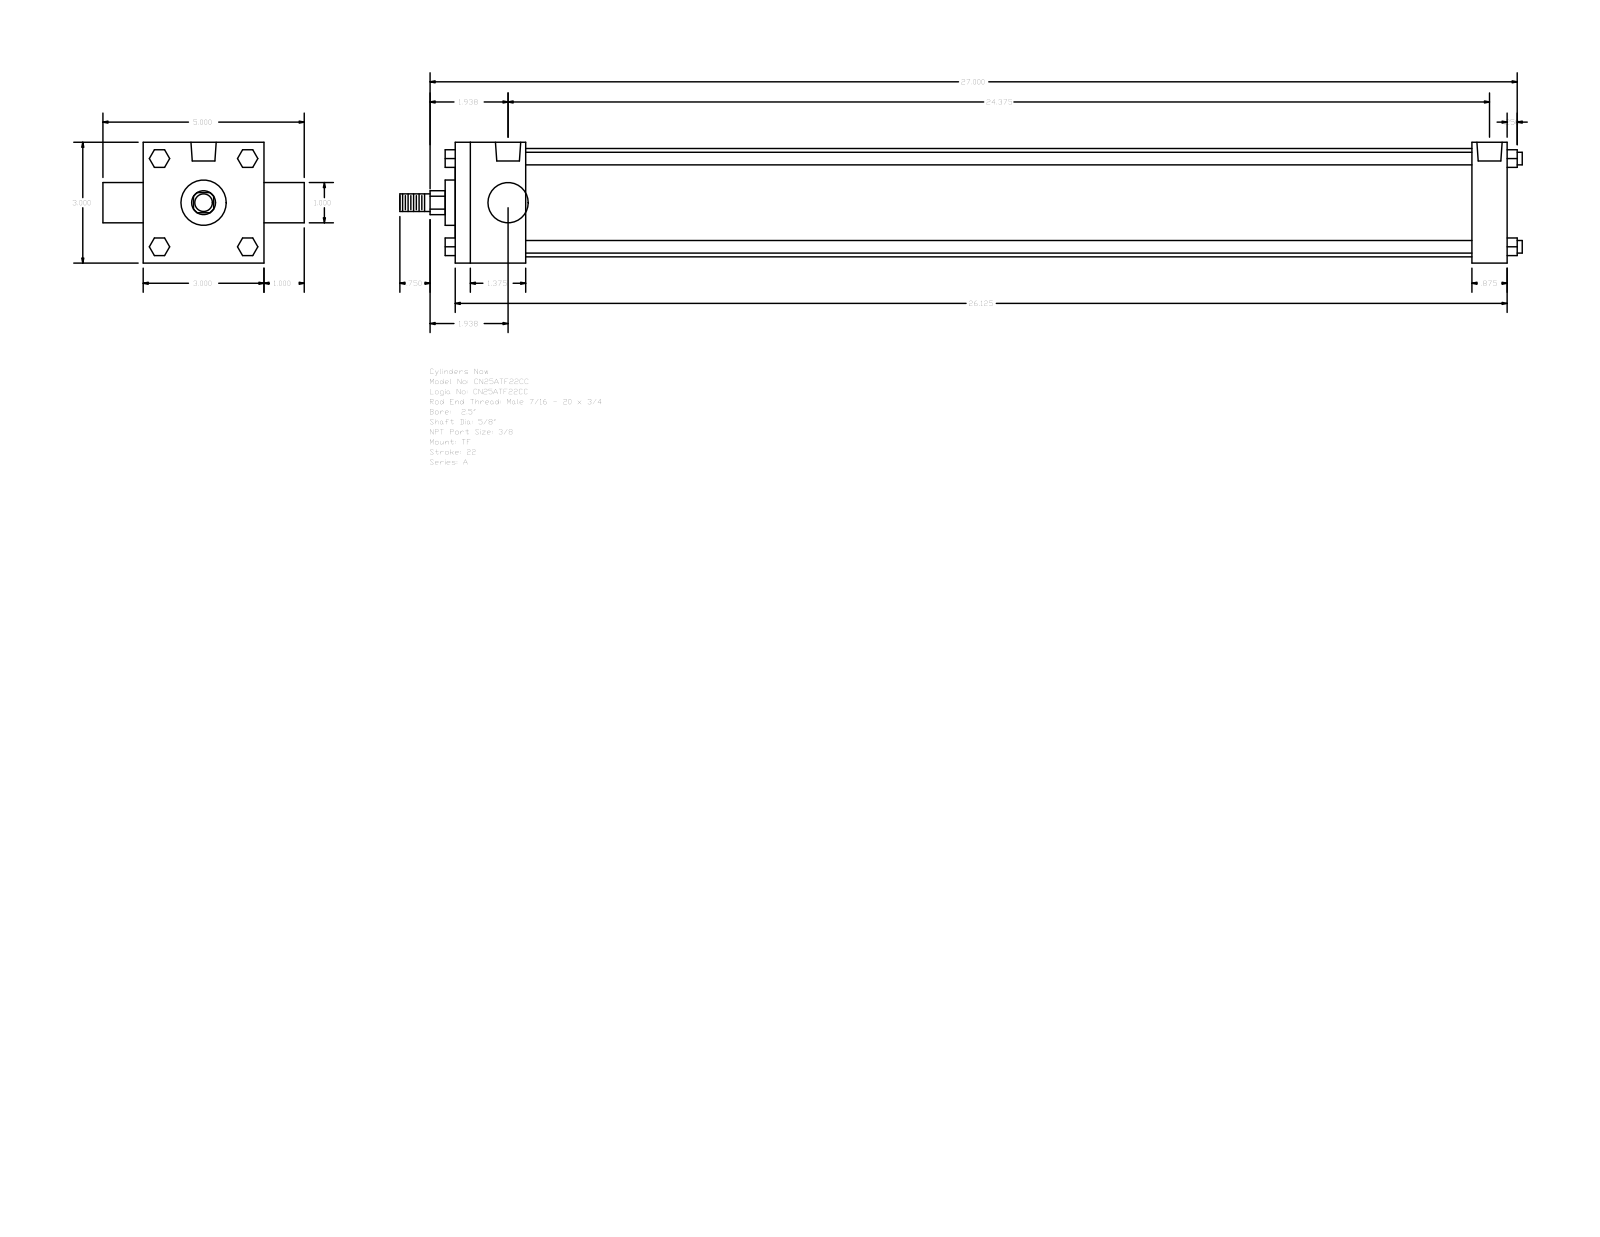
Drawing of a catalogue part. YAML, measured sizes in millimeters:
part_name: "A_TF__0250_0.625"
step_written_by: "GSSL Pune (CONFIG_CONTROL_DESIGN)"
units: millimeters
bodies: {solids: 0, faces: 120, planar: 92, cylindrical: 28, other: 0}
overall_size: [708.02, 127, 76.2]
round_holes:
  - {diameter: 5.56, count: 3}
  - {diameter: 15.93, count: 2}
round_bosses_or_shafts:
  - {diameter: 7.94, count: 4}
  - {diameter: 68.33, count: 1}
  - {diameter: 28.57, count: 1}
  - {diameter: 25.4, count: 1}
  - {diameter: 15.88, count: 1}
  - {diameter: 11.11, count: 1}
partial_cylinders:
  - {radius: 7.54, count: 1}
face_to_face_distances: [76.2, 663.57, 44.45, 641.35, 596.9, 619.12, 22.22, 25.4, 101.6, 6.35]
hole_center_spacings: [2.38, 621.51, 619.13, 623.89]
